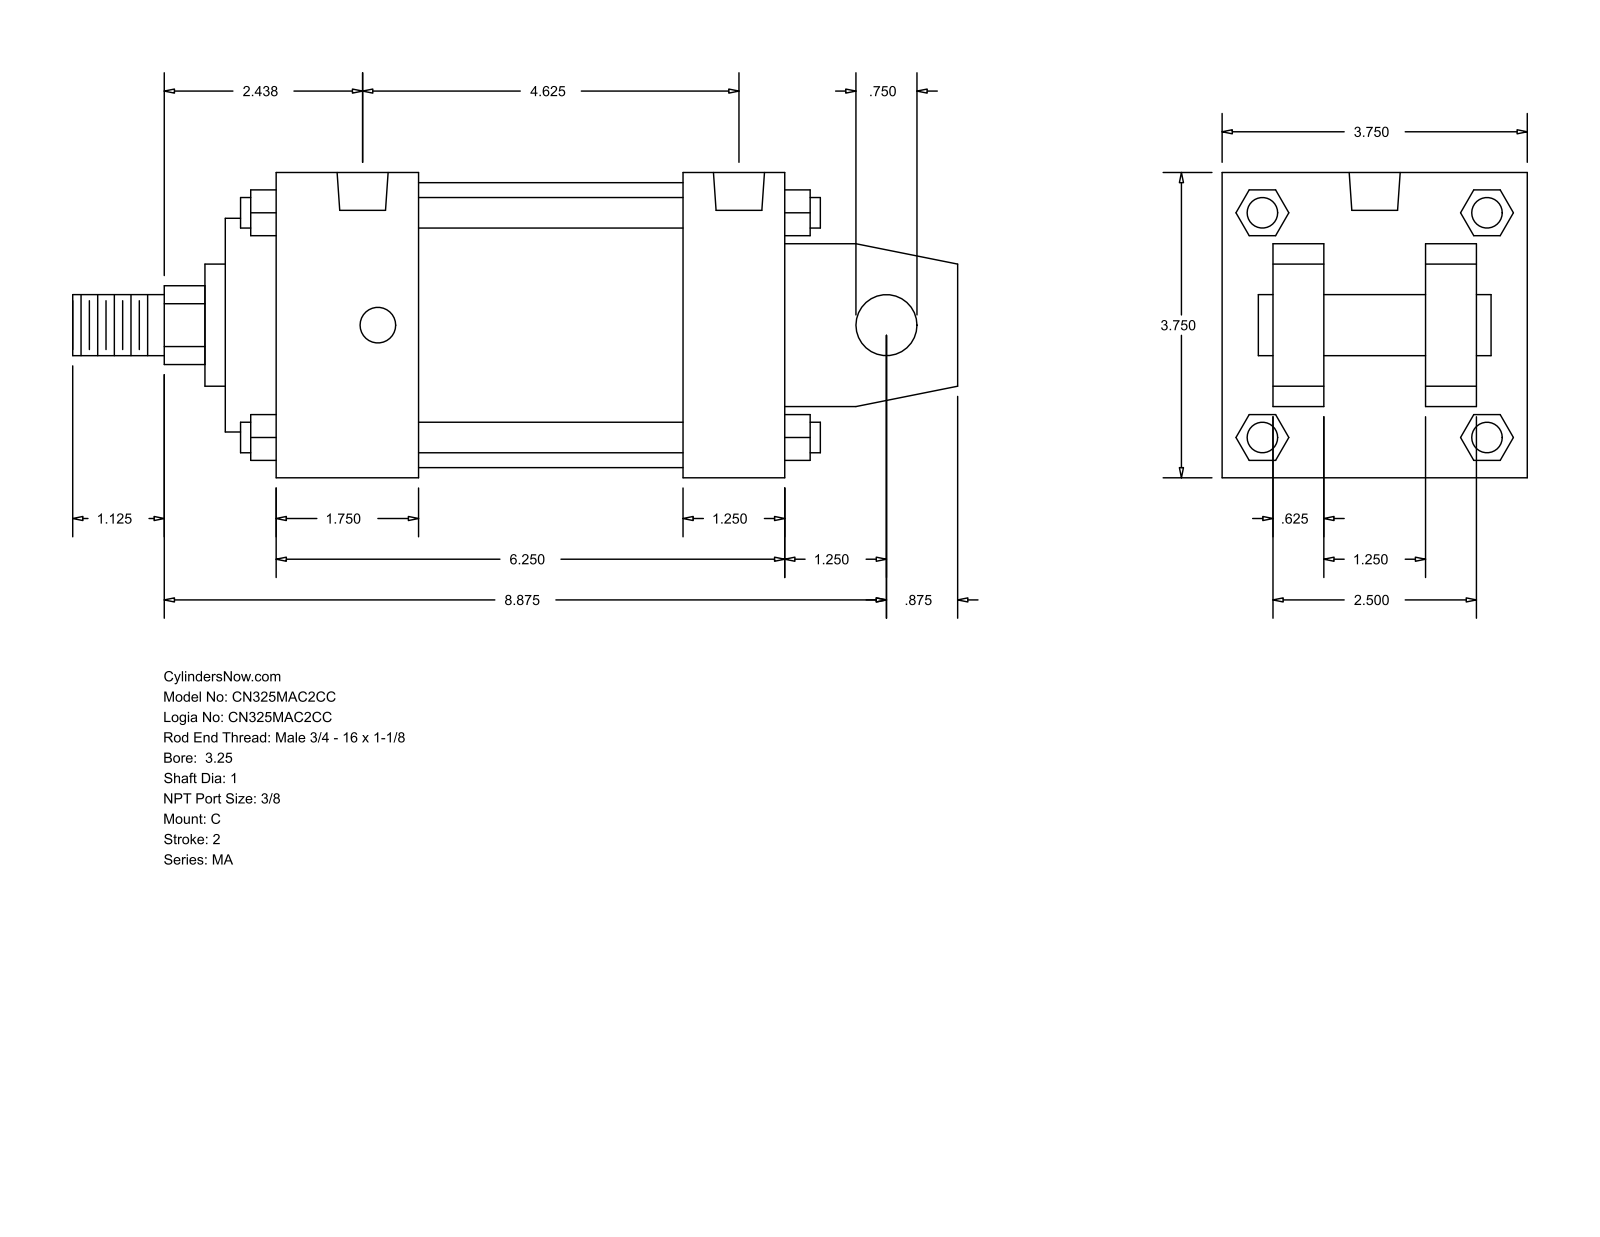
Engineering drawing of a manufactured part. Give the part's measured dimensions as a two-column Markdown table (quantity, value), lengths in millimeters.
| quantity | value |
| --- | --- |
| part name | MA_C__0325_1 |
| STEP written by | GSSL Pune (CONFIG_CONTROL_DESIGN) |
| units | millimeters |
| bodies | 0 solids, 141 faces (109 planar, 32 cylindrical, 0 other) |
| overall size | 276.23 × 95.25 × 95.25 |
| round holes (diameter × count) | 11.11 × 4, 15.93 × 2 |
| round bosses / shafts (diameter × count) | 9.53 × 4, 19.05 × 2, 88.9 × 1, 66.67 × 1, 38.1 × 1, 25.4 × 1 |
| partial cylindrical surfaces (radius × count) | 12.29 × 1 |
| main face-to-face distances | 95.24, 15.87, 63.5, 158.76, 31.74, 79.37, 47.63, 127.01, 31.75, 44.46 |
| hole center spacings | 107.95, 4.76, 4.77, 112.71, 112.72, 117.48 |
